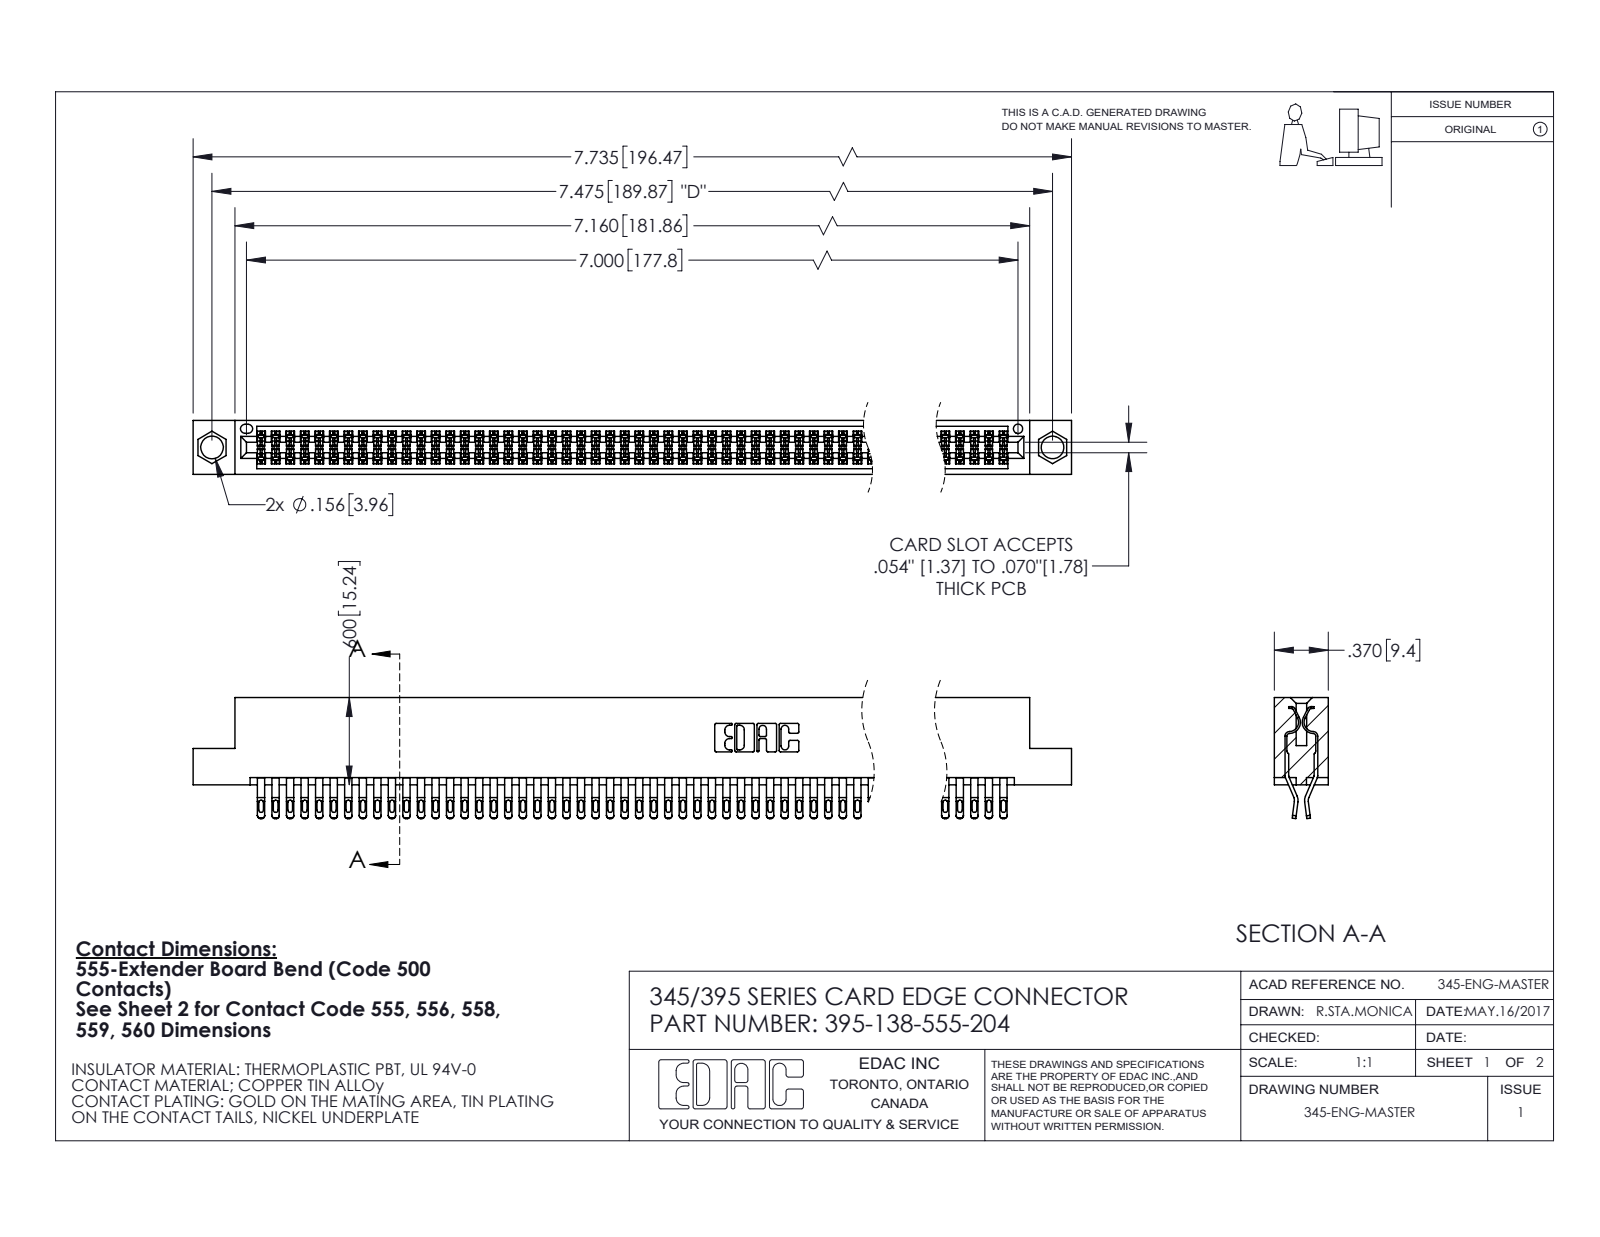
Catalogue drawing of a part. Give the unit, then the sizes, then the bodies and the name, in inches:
Units: inches
Overall size (bounding box): 7.735 × 0.832 × 0.37
Round holes (diameter × count): ⌀0.156 ×2, ⌀0.064 ×1
Partial cylindrical surfaces — rounded edges, fillets, slot ends (radius × count): R0.016 ×345, R0.006 ×276, R0.02 ×276, R0.01 ×22, R0.007 ×6, R0.031 ×6, R0.026 ×3, R0.01 ×2
Main face-to-face distances: 0.298, 0.072, 0.025, 0.37, 0.2, 0.098, 0.272, 0.225, 0.175, 0.149
Hole centre spacings: 0.27, 7.239, 7.475
Volume: 1.198 in³ · Surface area: 47.71 in²
Bodies: 139 solids, 7868 faces (4372 planar, 3496 cylindrical, 0 other)
Part name (STEP PRODUCT): 345-292-001_555 Tail; 395-138-555-204; 345 Part_Flush Mounting Lugs - 0.156 Dia-TI
STEP written by: SolidWorks 2020 (CONFIG_CONTROL_DESIGN)
